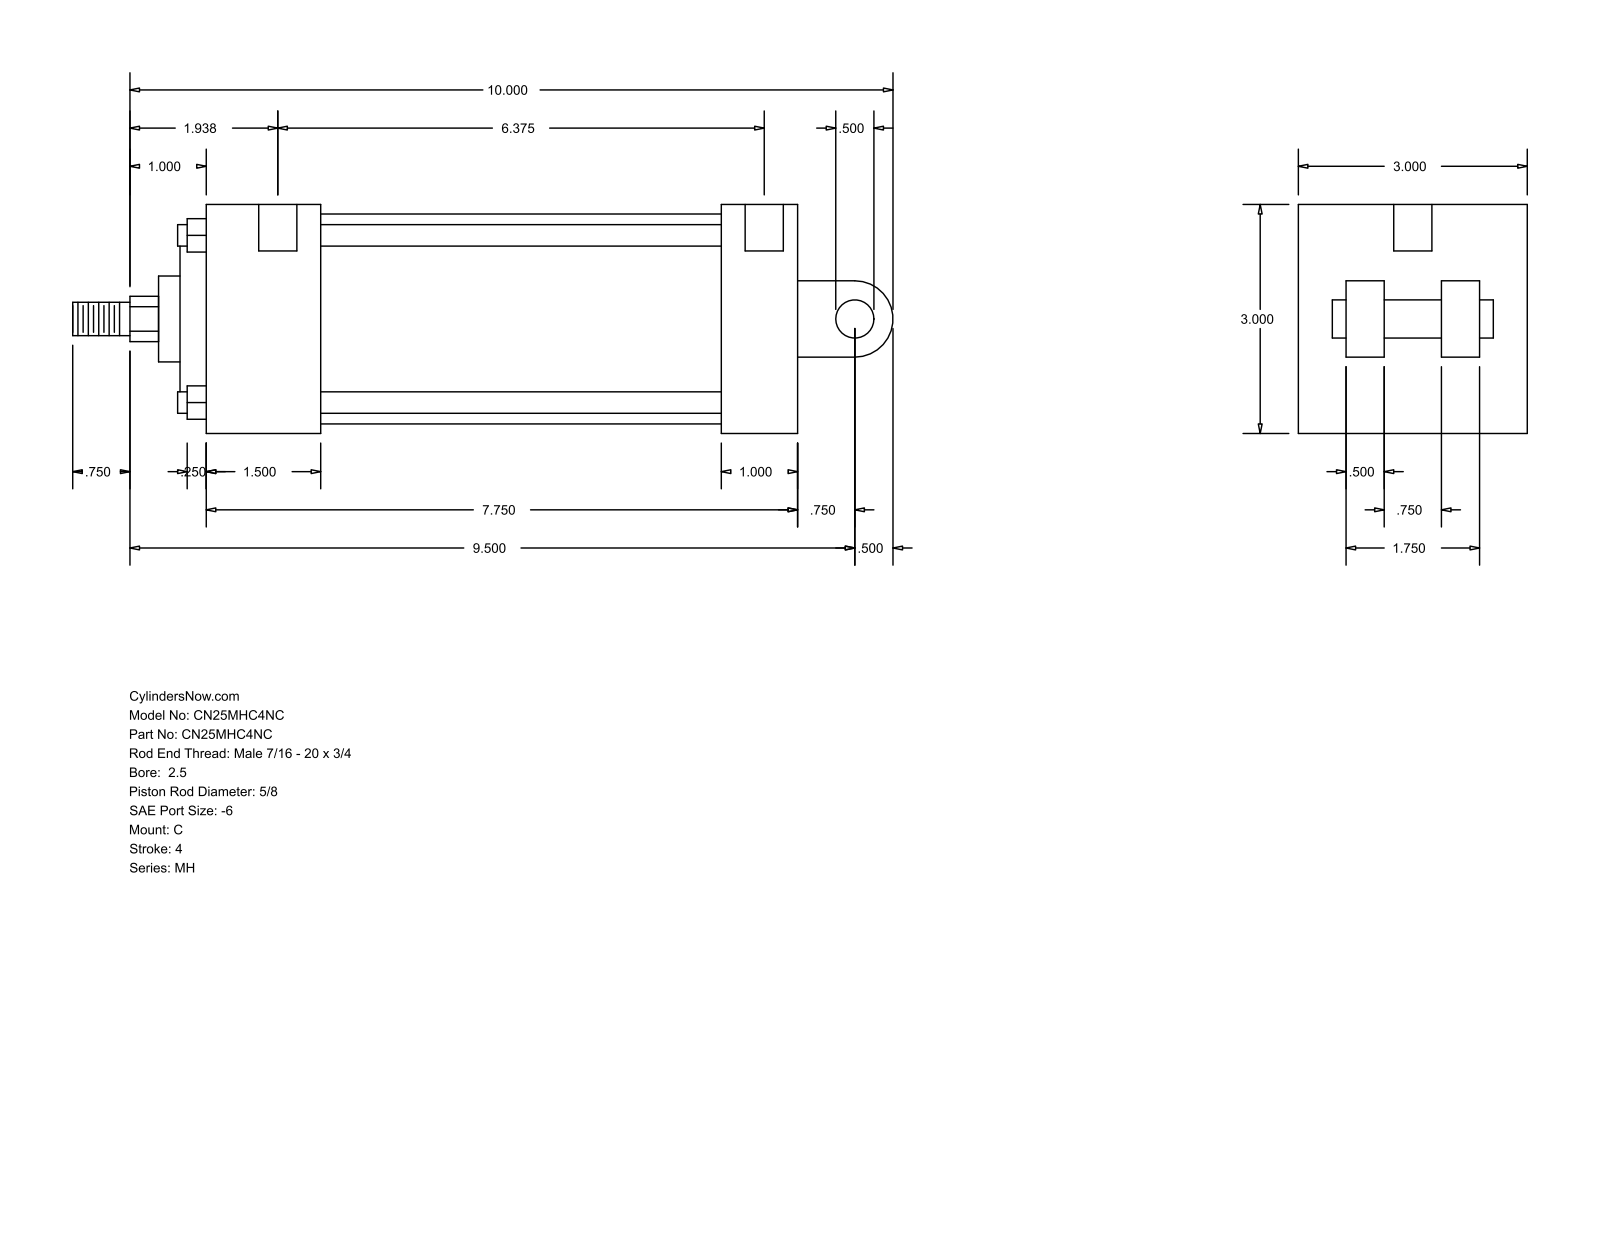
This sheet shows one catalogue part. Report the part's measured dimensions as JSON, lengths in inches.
{"part_name": "MH_C__0250_0.625", "step_written_by": "GSSL Pune (CONFIG_CONTROL_DESIGN)", "units": "inches", "bodies": {"solids": 0, "faces": 101, "planar": 71, "cylindrical": 30, "other": 0}, "overall_size": [10.75, 3, 3], "round_holes": [[0.219, 4], [0.5, 2]], "round_bosses_or_shafts": [[0.281, 4], [2.75, 1], [2.187, 1], [1.125, 1], [0.625, 1], [0.5, 1], [0.437, 1]], "partial_cylinders_radius": [[0.297, 1], [0.5, 1]], "face_to_face_distances": [3, 1, 7.75, 0.625, 1.5, 6.75, 5.25, 6.25, 0.344, 1.844], "hole_center_spacings": [6.687, 0.125, 0.187, 6.375, 6.5, 6.563]}
